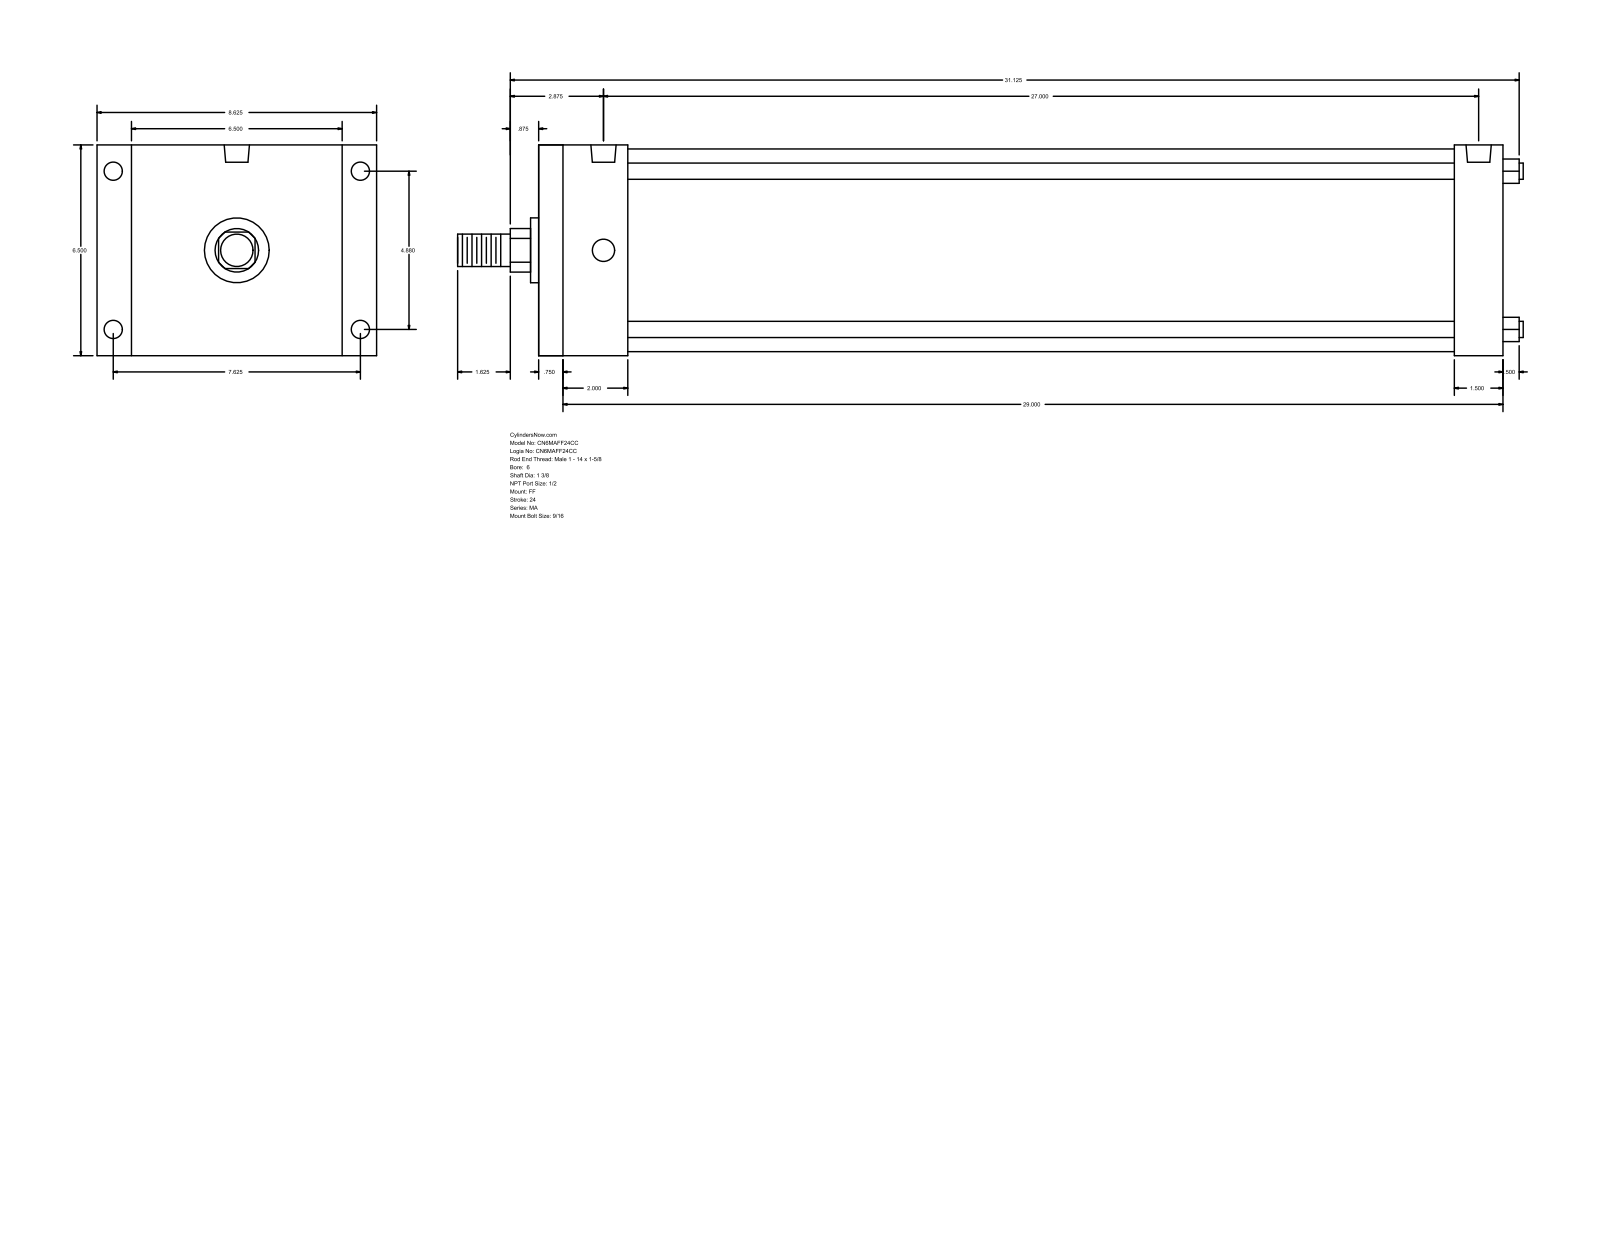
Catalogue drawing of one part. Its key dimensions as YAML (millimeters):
part_name: "MA_FF__0600_1.375"
step_written_by: "GSSL Pune (CONFIG_CONTROL_DESIGN)"
units: millimeters
bodies: {solids: 0, faces: 92, planar: 64, cylindrical: 28, other: 0}
overall_size: [835.02, 219.07, 165.1]
round_holes:
  - {diameter: 14.29, count: 4}
  - {diameter: 17.46, count: 4}
  - {diameter: 19.77, count: 2}
round_bosses_or_shafts:
  - {diameter: 12.7, count: 4}
  - {diameter: 158.75, count: 1}
  - {diameter: 50.8, count: 1}
  - {diameter: 34.92, count: 1}
  - {diameter: 25.4, count: 1}
partial_cylinders:
  - {radius: 17.06, count: 1}
face_to_face_distances: [165.1, 755.65, 15.87, 739.78, 66.67, 50.8, 688.98, 717.54, 701.67, 650.87]
hole_center_spacings: [123.96, 193.68, 229.95, 688.98, 3.18, 685.8]
